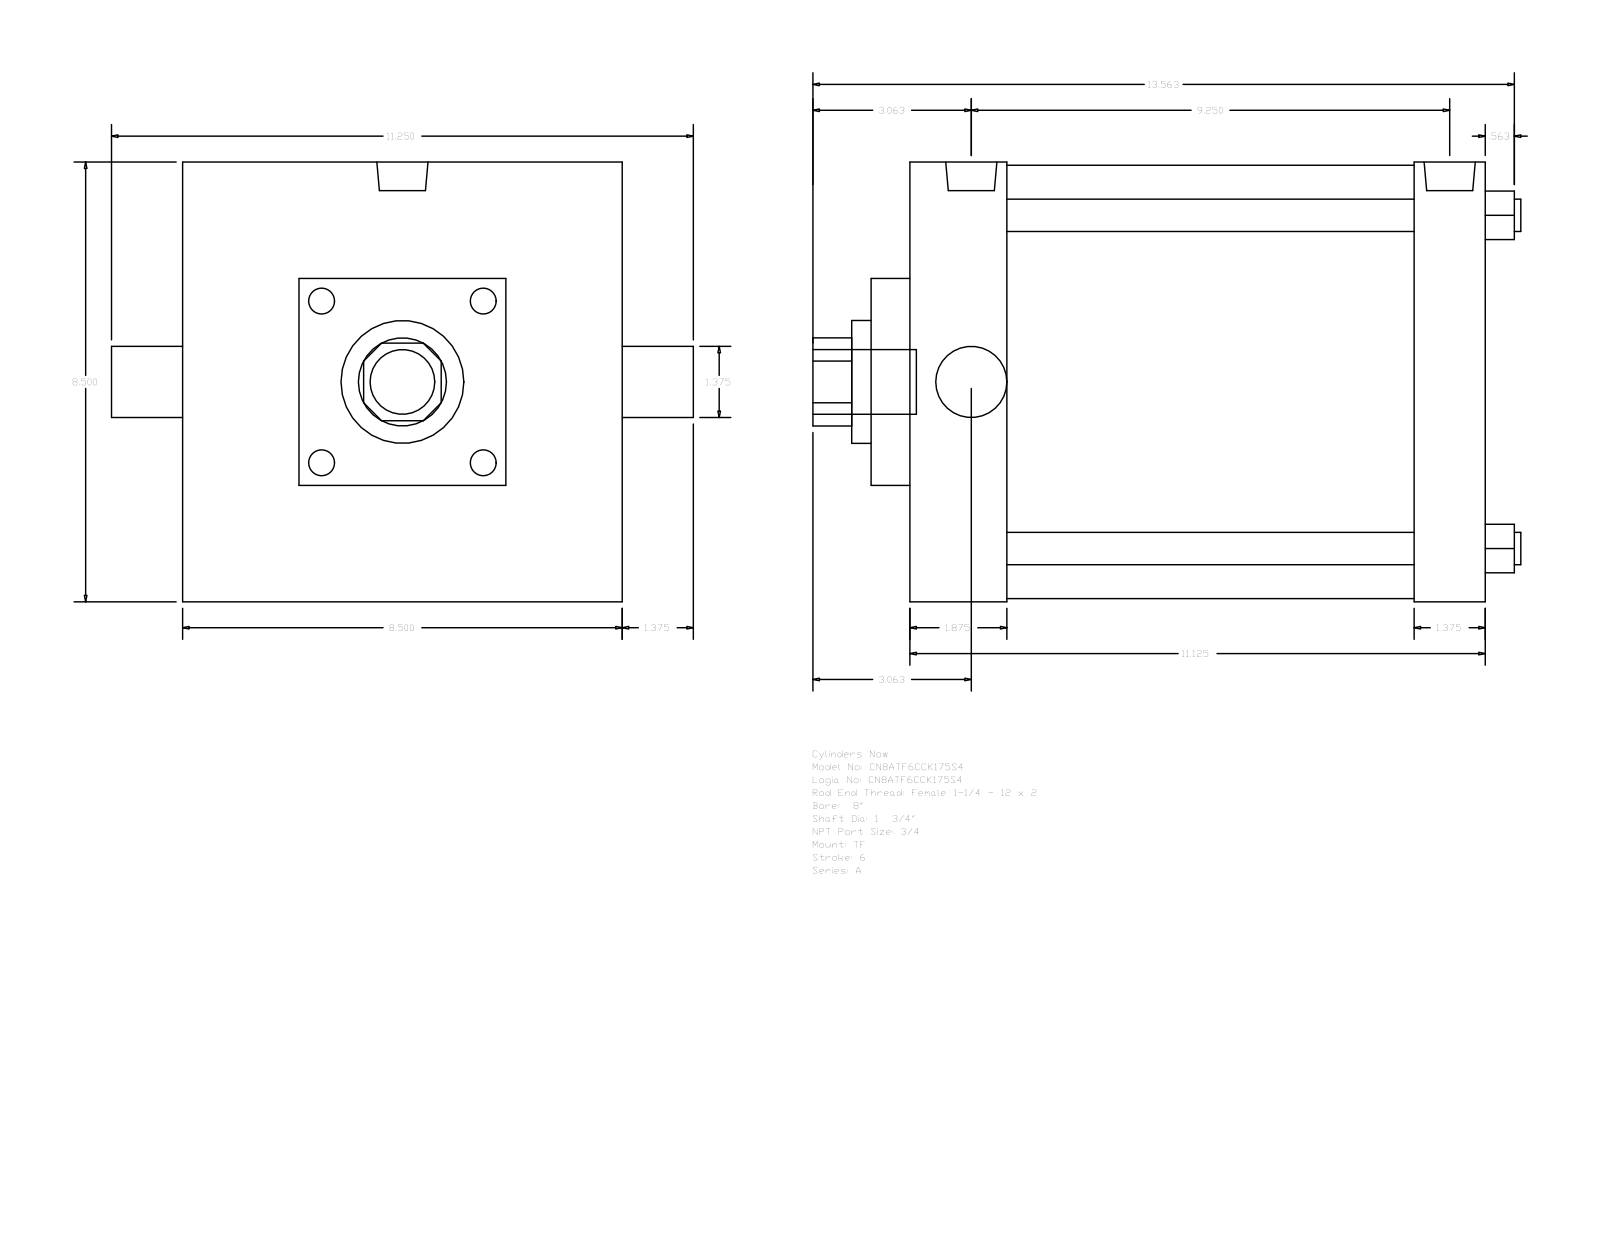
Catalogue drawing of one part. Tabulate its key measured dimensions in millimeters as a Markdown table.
| quantity | value |
| --- | --- |
| part name | A_TF__0800_1.75 |
| STEP written by | GSSL Pune (CONFIG_CONTROL_DESIGN) |
| units | millimeters |
| bodies | 0 solids, 89 faces (65 planar, 24 cylindrical, 0 other) |
| overall size | 347.66 × 285.75 × 215.9 |
| round holes (diameter × count) | 15.88 × 4, 34.92 × 1, 44.45 × 1, 60.33 × 1, 212.72 × 1 |
| round bosses / shafts (diameter × count) | 15.08 × 3, 25.12 × 2, 31.75 × 1 |
| partial cylindrical surfaces (radius × count) | 21.63 × 1 |
| main face-to-face distances | 282.58, 215.9, 34.93, 47.63, 234.95, 247.65, 200.02, 19.05, 57.15, 158.75 |
| hole center spacings | 115.67, 163.58, 231.34 |
